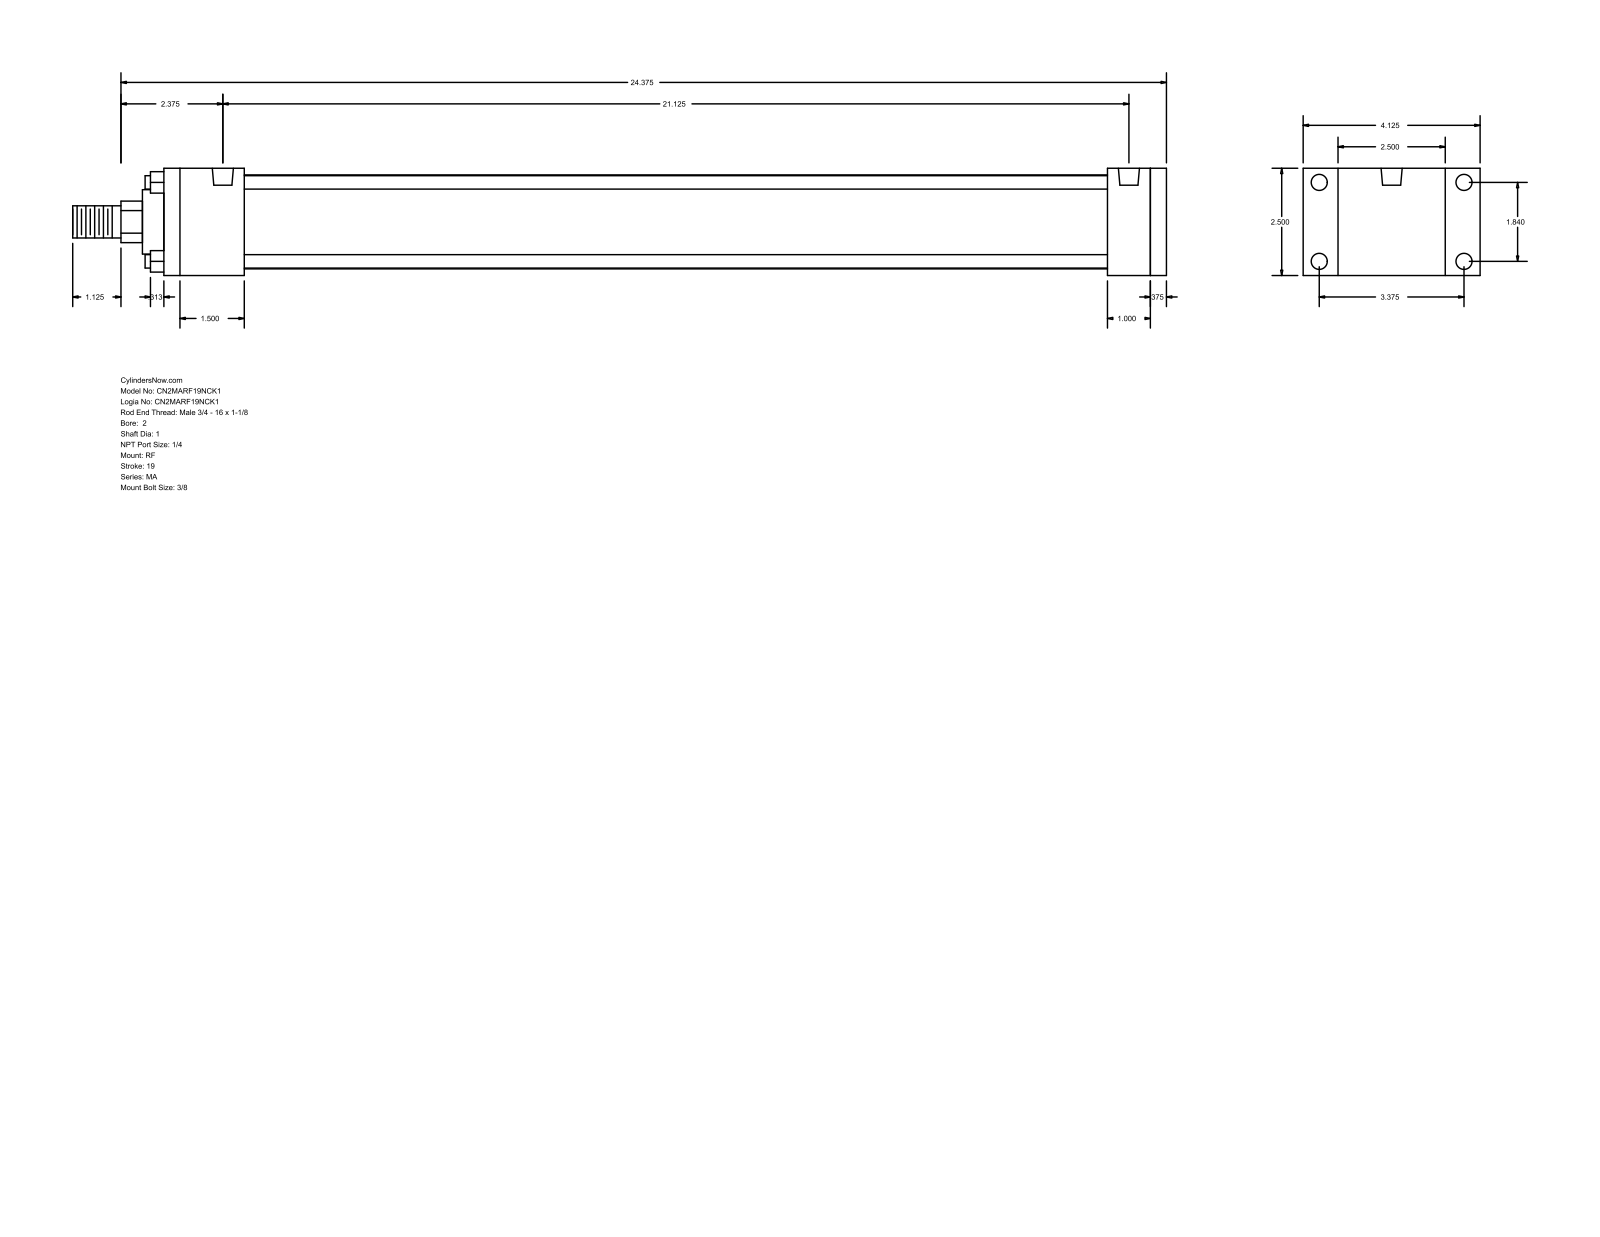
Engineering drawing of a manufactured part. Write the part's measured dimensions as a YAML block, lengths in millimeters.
part_name: "MA_RF__0200_1"
step_written_by: "GSSL Pune (CONFIG_CONTROL_DESIGN)"
units: millimeters
bodies: {solids: 0, faces: 92, planar: 64, cylindrical: 28, other: 0}
overall_size: [647.7, 104.78, 63.5]
round_holes:
  - {diameter: 7.94, count: 4}
  - {diameter: 9.53, count: 4}
  - {diameter: 12.49, count: 2}
round_bosses_or_shafts:
  - {diameter: 7.94, count: 4}
  - {diameter: 55.63, count: 1}
  - {diameter: 38.1, count: 1}
  - {diameter: 25.4, count: 1}
  - {diameter: 19.05, count: 1}
partial_cylinders:
  - {radius: 12.29, count: 1}
face_to_face_distances: [63.5, 584.2, 9.52, 593.72, 25.4, 20.64, 12.7, 47.63, 536.57, 546.09]
hole_center_spacings: [46.74, 85.72, 97.63, 536.57]
